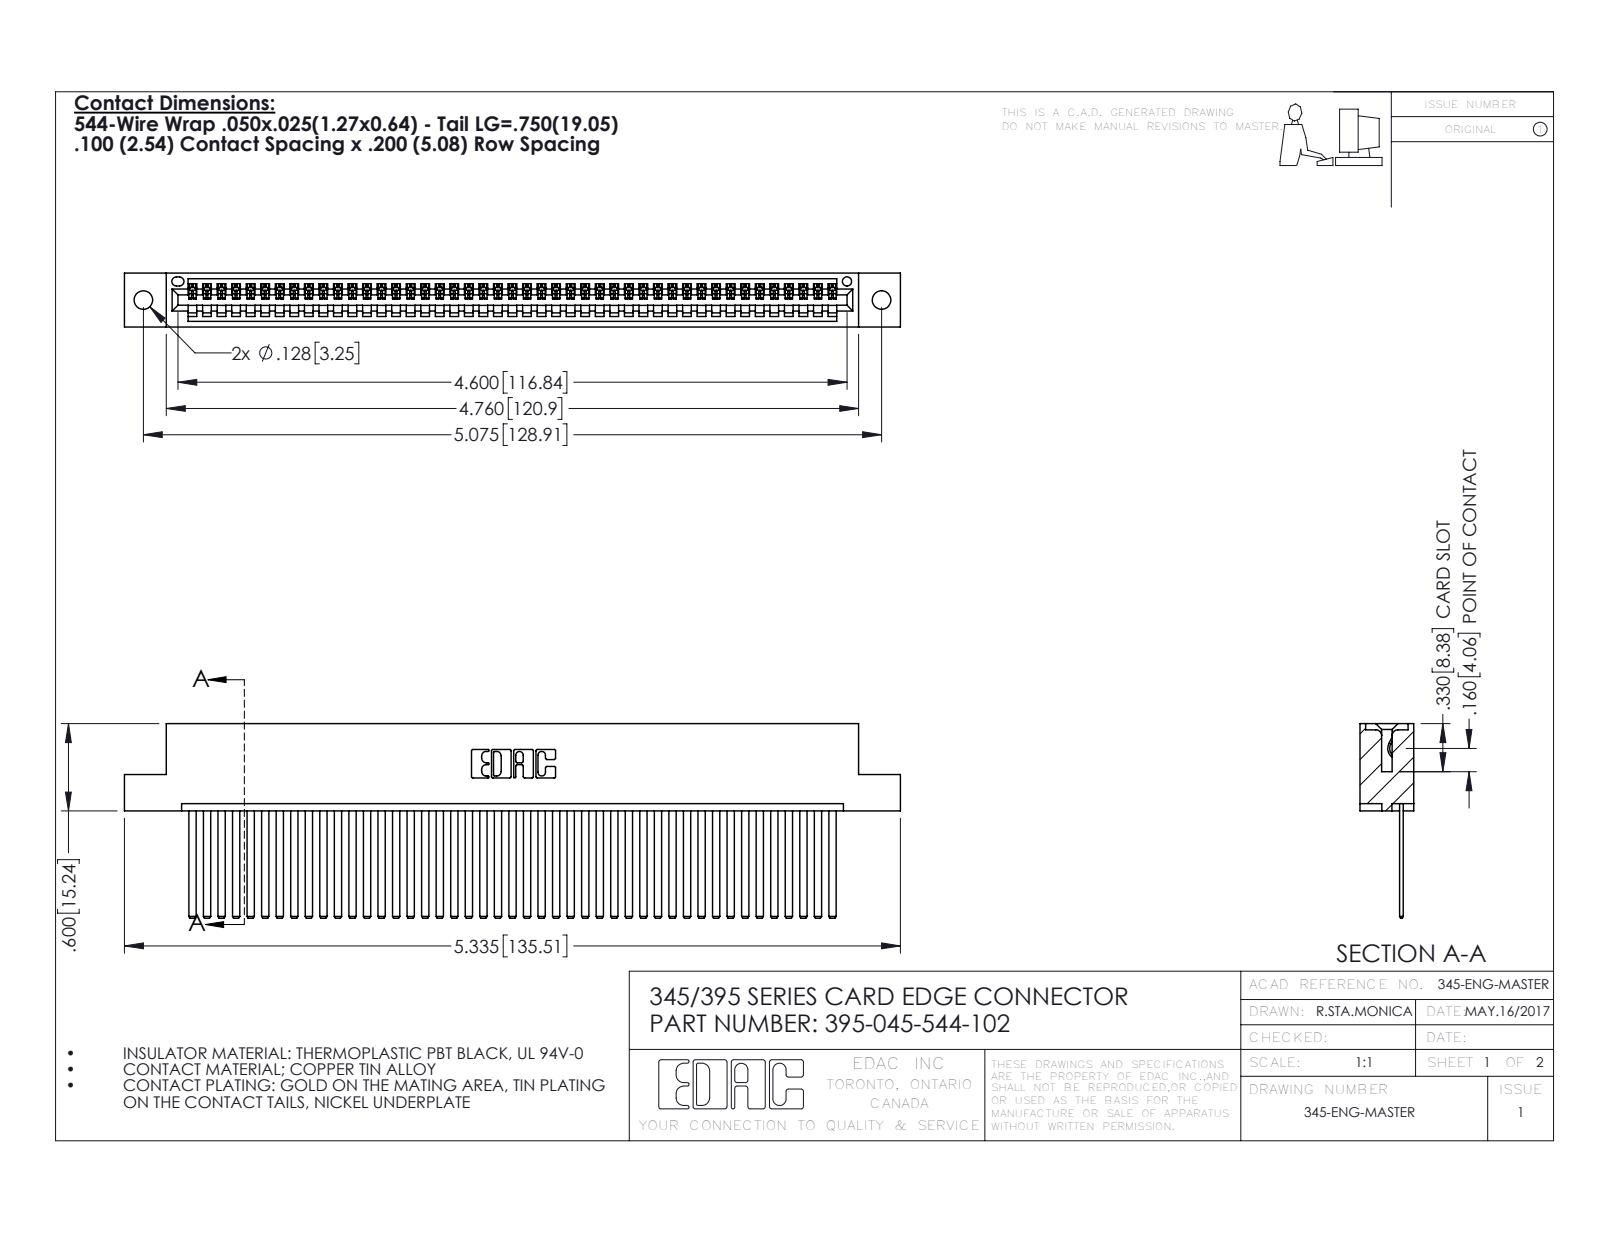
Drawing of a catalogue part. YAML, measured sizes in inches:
part_name: "345-292-001_345-293-144; 395-045-544-102; 345 Part_Flush Mounting Lugs - 0.128 Dia"
step_written_by: "SolidWorks 2016 (CONFIG_CONTROL_DESIGN)"
units: inches
bodies: {solids: 46, faces: 2466, planar: 1700, cylindrical: 766, other: 0}
overall_size: [5.335, 1.337, 0.37]
volume: 0.816
surface_area: 29.63
round_holes:
  - {diameter: 0.128, count: 2}
  - {diameter: 0.064, count: 1}
partial_cylinders:
  - {radius: 0.006, count: 90}
  - {radius: 0.01, count: 22}
  - {radius: 0.007, count: 6}
  - {radius: 0.031, count: 6}
  - {radius: 0.026, count: 3}
  - {radius: 0.031, count: 2}
  - {radius: 0.04, count: 2}
  - {radius: 0.014, count: 1}
face_to_face_distances: [0.072, 0.298, 0.025, 0.098, 0.272, 0.37, 0.2, 0.225, 0.149, 0.072]
hole_center_spacings: [0.27, 4.839, 5.075]
